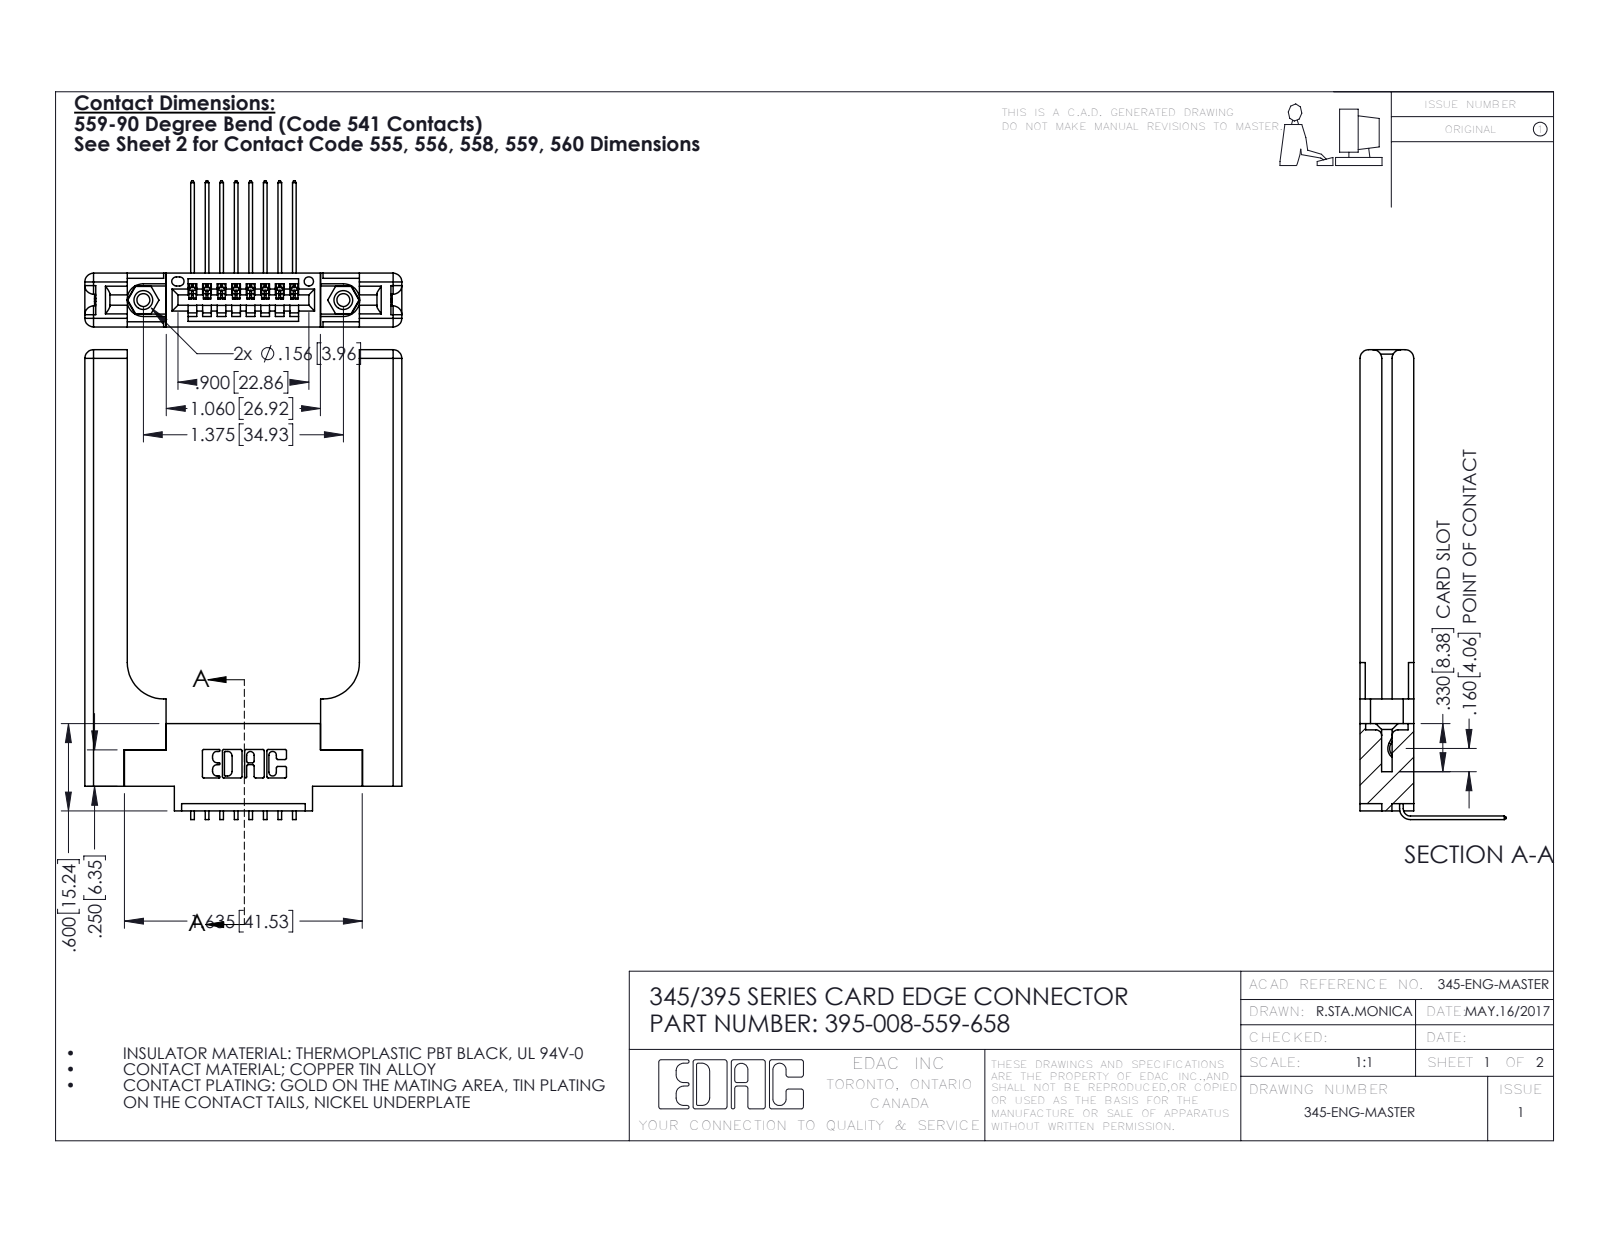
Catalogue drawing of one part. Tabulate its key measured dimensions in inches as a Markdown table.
| quantity | value |
| --- | --- |
| part name | 345-250-001_345-250-001-102; 345-292-001_558 559 Tail - 1; 395-008-559-658; 345-220-058_345-220-058 (+1 more) |
| STEP written by | SolidWorks 2016 (CONFIG_CONTROL_DESIGN) |
| units | inches |
| bodies | 13 solids, 866 faces (568 planar, 238 cylindrical, 60 other) |
| overall size | 3.229 × 2.179 × 1.005 |
| volume | 0.818 in³ |
| surface area | 18.02 in² |
| round holes (diameter × count) | 0.089 × 2, 0.125 × 2, 0.156 × 2, 0.064 × 1 |
| round bosses / shafts (diameter × count) | 0.155 × 2 |
| partial cylindrical surfaces (radius × count) | 0.01 × 22, 0.006 × 16, 0.06 × 16, 0.007 × 6, 0.031 × 6, 0.026 × 3, 0.03 × 2, 0.031 × 2 |
| main face-to-face distances | 0.37, 0.15, 0.22, 0.072, 0.148, 0.077, 0.298, 1.596, 0.071, 0.12 |
| hole center spacings | 0.27, 1.144, 1.375 |
